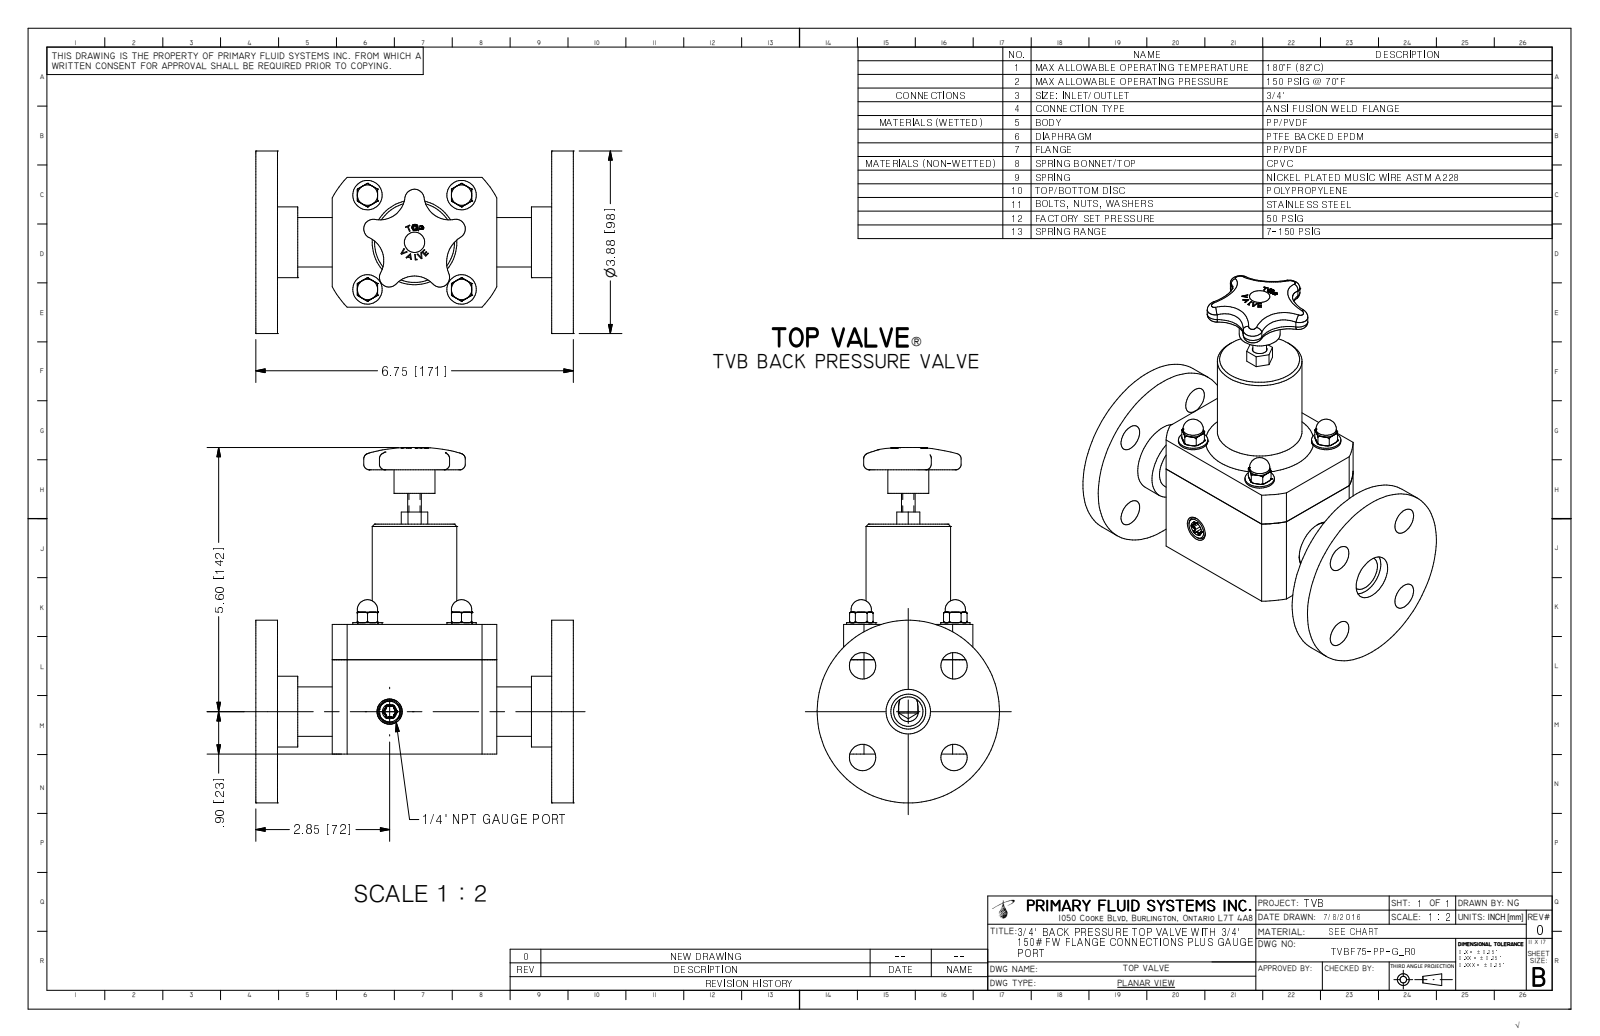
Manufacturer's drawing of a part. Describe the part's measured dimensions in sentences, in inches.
The part is named "TVBF75-PP-G_R0". Its 3-D file was written by "Autodesk Inventor 2009 (AUTOMOTIVE_DESIGN)". It is 1 solid with 383 faces: 160 planar, 67 cylindrical and 156 other. Overall it measures 7.539 by 6.75 by 3.875 inches. Its volume is 43.67 cubic inches and its surface area 154.5 square inches. Round holes: 4 of diameter 0.175, 4 of diameter 0.56, 1 of diameter 0.742, 1 of diameter 0.945. Round bosses or shafts: 4 of diameter 0.625, 4 of diameter 0.433, 4 of diameter 0.375, 1 of diameter 3.875, 1 of diameter 1.8, 1 of diameter 1.5, 1 of diameter 1.05, 1 of diameter 0.87. Partial cylindrical surfaces (rounded edges, fillets, slot ends): 6 of radius 0.027, 5 of radius 0.085, 5 of radius 0.205, 4 of radius 0.536, 4 of radius 0.656, 1 of radius 0.625, 1 of radius 0.745, 1 of radius 1.988. The main face-to-face distances are 0.46, 6.29, 6.75, 5.83, 1.625, 5.125, 1.165, 4.665, 2.75, 3.5. The hole center spacings are 1.375, 1.945, 2, 2.75, 2.828.
